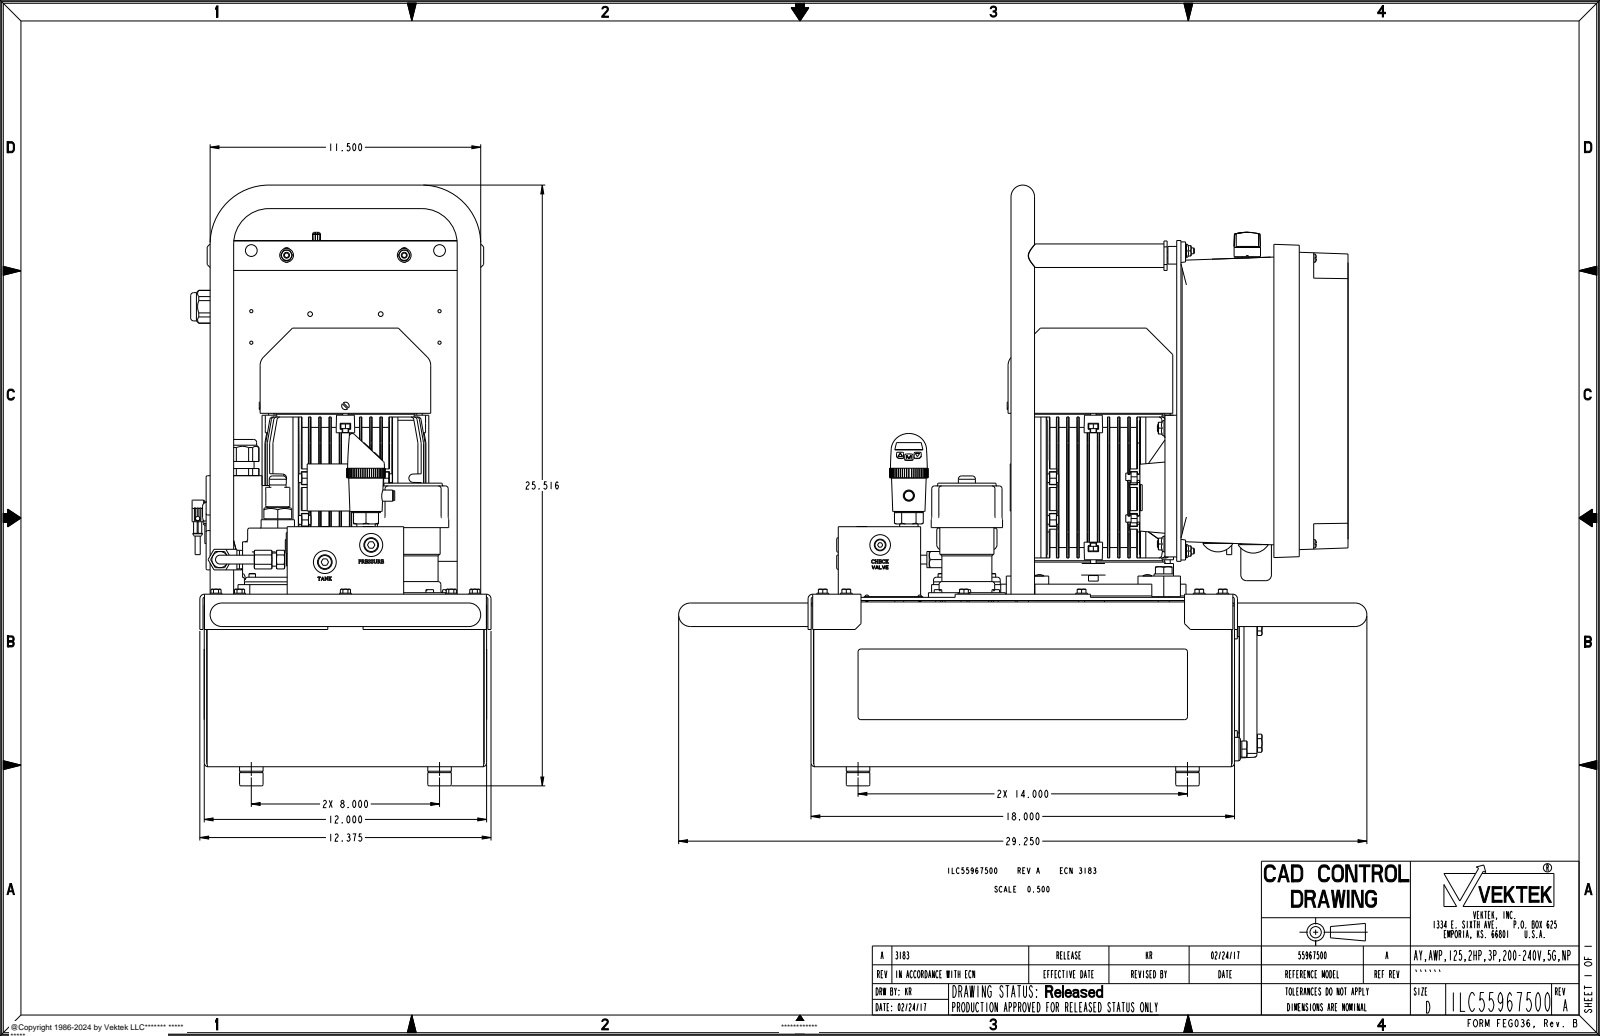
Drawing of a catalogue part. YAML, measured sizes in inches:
part_name: "ILC55967500"
step_written_by: "PRO/ENGINEER BY PARAMETRIC TECHNOLOGY CORPORATION, 2013320 (AUTOMOTIVE_DESIGN)"
units: inches
bodies: {solids: 10, faces: 9227, planar: 4243, cylindrical: 2490, other: 2494}
overall_size: [29.25, 25.516, 12.764]
volume: 786.5
surface_area: 5193
round_holes:
  - {diameter: 0.312, count: 14}
  - {diameter: 0.344, count: 14}
  - {diameter: 0.118, count: 8}
  - {diameter: 0.75, count: 8}
  - {diameter: 0.218, count: 6}
  - {diameter: 0.354, count: 6}
  - {diameter: 0.472, count: 6}
  - {diameter: 0.5, count: 6}
  - {diameter: 0.875, count: 6}
  - {diameter: 0.079, count: 5}
  - {diameter: 0.165, count: 5}
  - {diameter: 0.236, count: 5}
round_bosses_or_shafts:
  - {diameter: 0.25, count: 24}
  - {diameter: 1, count: 14}
  - {diameter: 0.5, count: 14}
  - {diameter: 0.375, count: 9}
  - {diameter: 0.197, count: 9}
  - {diameter: 0.177, count: 9}
  - {diameter: 0.35, count: 8}
  - {diameter: 0.472, count: 7}
partial_cylinders:
  - {radius: 0.118, count: 124}
  - {radius: 0.02, count: 82}
  - {radius: 0.039, count: 55}
  - {radius: 0.005, count: 54}
  - {radius: 0.079, count: 41}
  - {radius: 0.157, count: 31}
  - {radius: 0.197, count: 21}
  - {radius: 0.108, count: 18}
face_to_face_distances: [0.105, 0.138, 11.895, 7.06, 6.955, 17.895, 0.165, 0.135, 11.79, 6.992]
hole_center_spacings: [1.581, 14.867, 8, 4.2, 4.272, 4.5, 4.593, 5.335]
